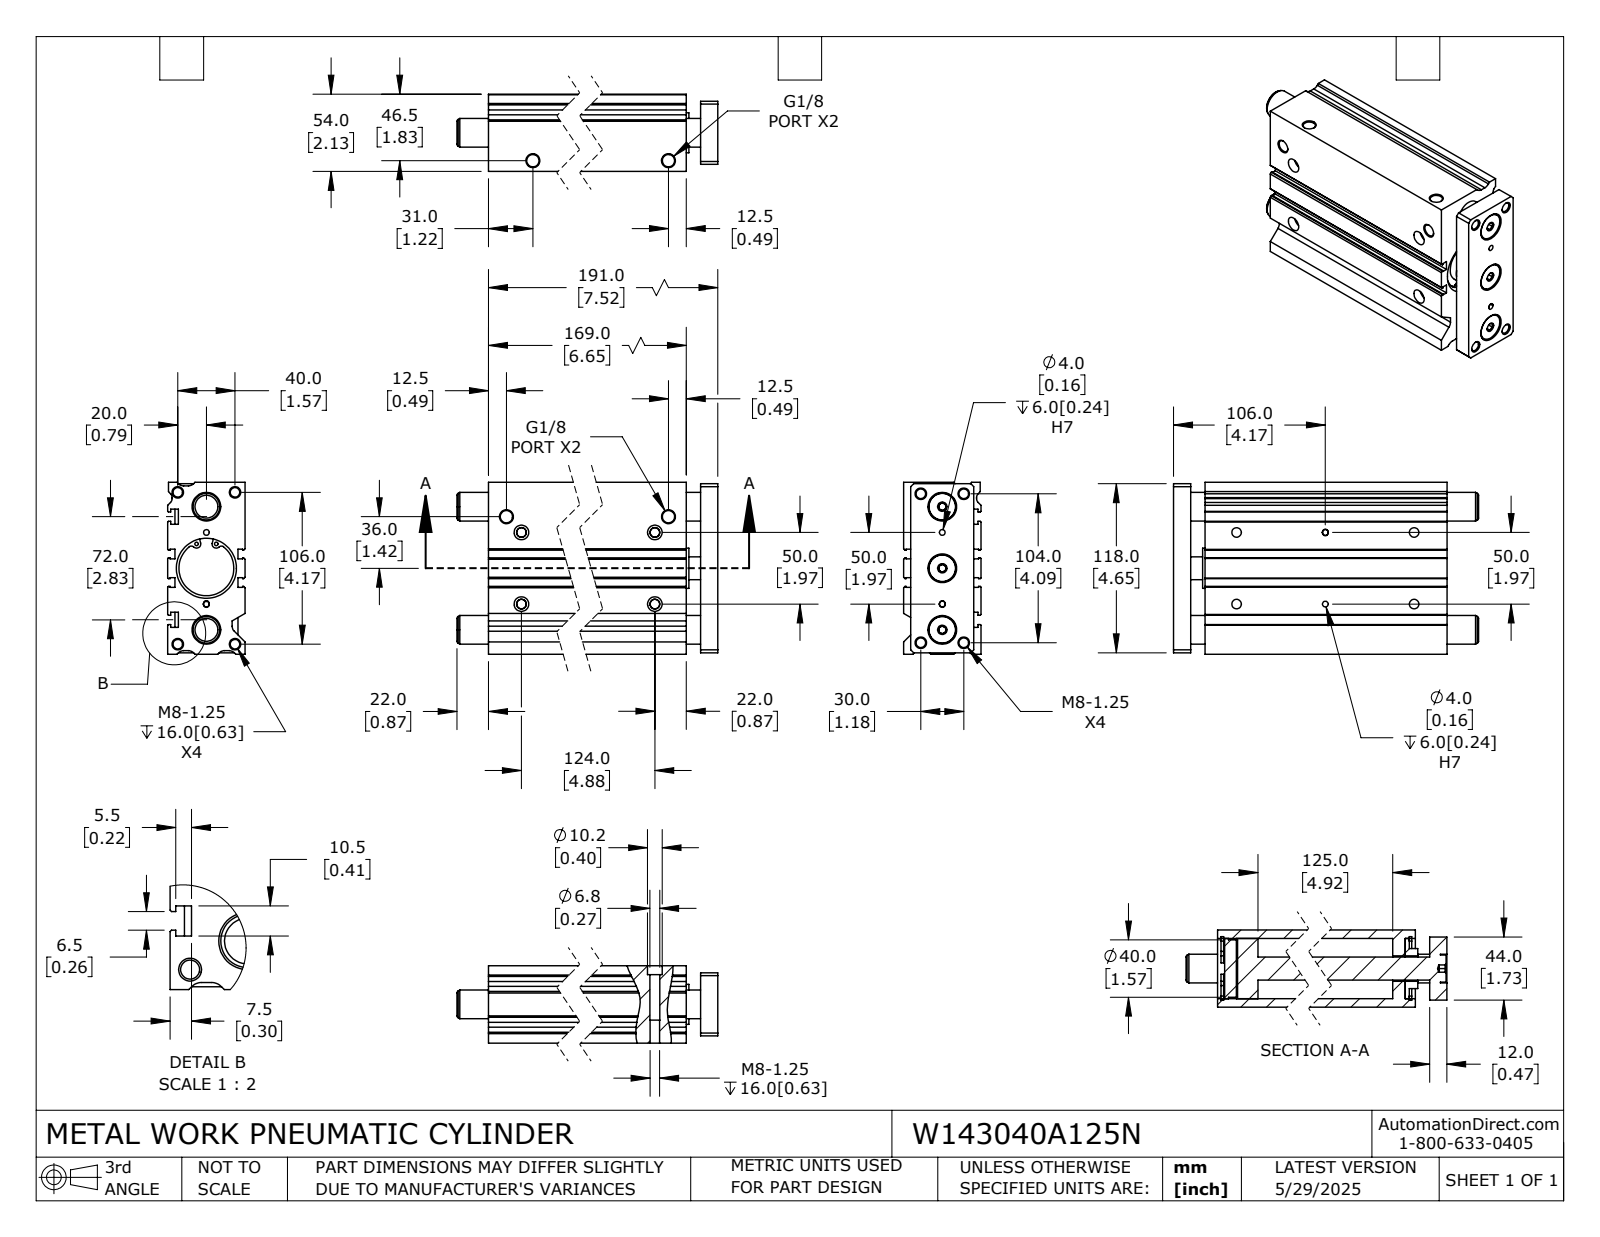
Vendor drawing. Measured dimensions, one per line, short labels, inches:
name: W143040A125N; W143040A125N_ROD; W143040A125N_BODY
written by: SolidWorks 2024 (CONFIG_CONTROL_DESIGN)
unit: in
bodies: 6 solids, 393 faces (192 planar, 151 cylindrical, 50 other)
size: 8.386 × 4.724 × 2.126
volume: 56.45 in³; area: 311.8 in²
holes: 12× ⌀0.262, 4× ⌀0.098, 4× ⌀0.157, 4× ⌀0.268, 4× ⌀0.337, 4× ⌀0.402, 3× ⌀0.197, 3× ⌀0.787, 1× ⌀0.697, 1× ⌀1.51
bosses: 3× ⌀0.748, 2× ⌀1.752, 1× ⌀1.654, 1× ⌀1.575, 1× ⌀1.102, 1× ⌀0.63
rounds: 7× R0.197, 4× R0.079, 4× R0.089, 4× R0.116, 2× R0.157
face distances: 2.126, 0.197, 1.929, 0.098, 4.724, 0.866, 7.52, 0.472, 0.394, 7.047
hole spacings: 0.201, 0.415, 0.689, 0.722, 0.88, 1.059, 1.216, 1.355
